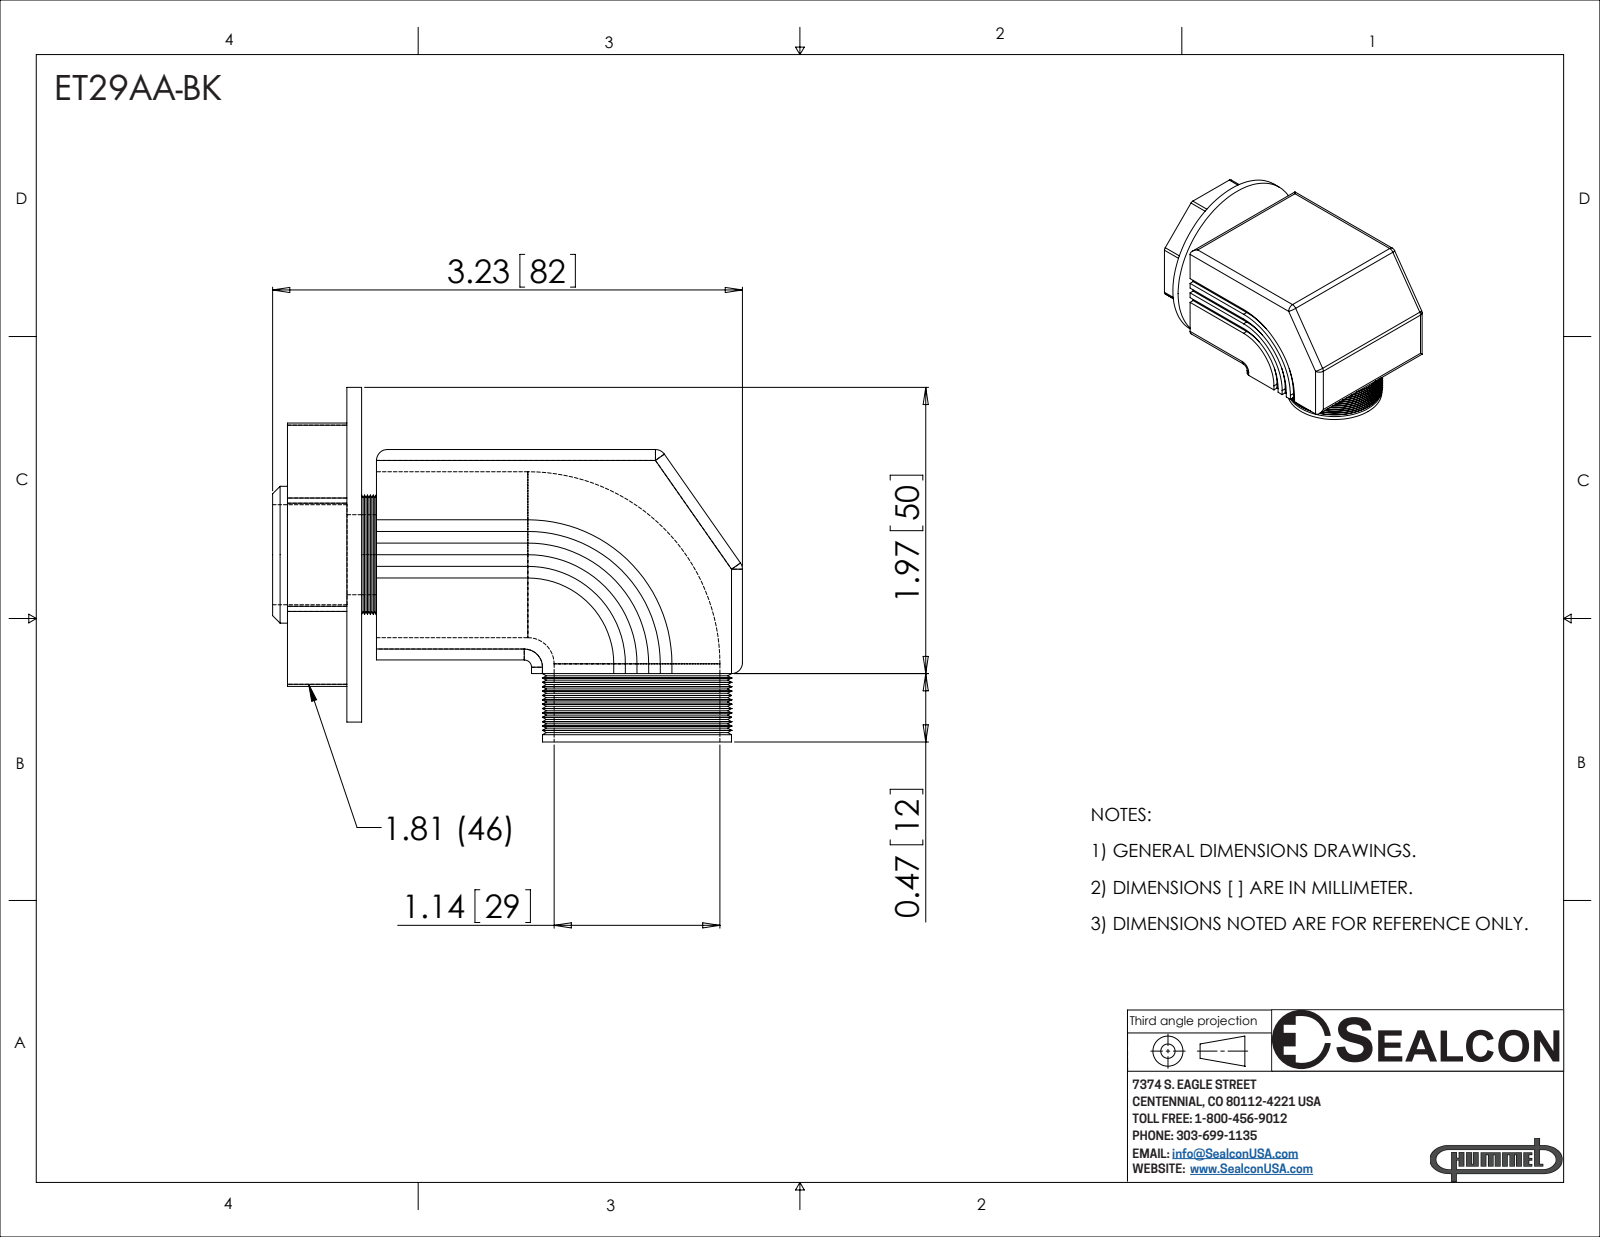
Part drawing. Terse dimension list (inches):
name: ET29AA-BK
written by: SolidWorks 2008 (CONFIG_CONTROL_DESIGN)
unit: in
bodies: 4 solids, 229 faces (62 planar, 53 cylindrical, 114 other)
size: 3.23 × 2.437 × 2.3
volume: 6.361 in³; area: 49.77 in²
holes: 2× ⌀1.14, 1× ⌀0.55, 1× ⌀0.687
bosses: 1× ⌀2.3, 1× ⌀0.94, 1× ⌀0.82
rounds: 14× R0.075, 9× R0.05, 1× R0.59, 1× R0.67, 1× R0.75, 1× R0.83, 1× R0.91, 1× R0.99
face distances: 2.04, 0.51, 1.54, 0.102, 0.612, 1.446, 0.094, 0.102, 0.408, 0.204
